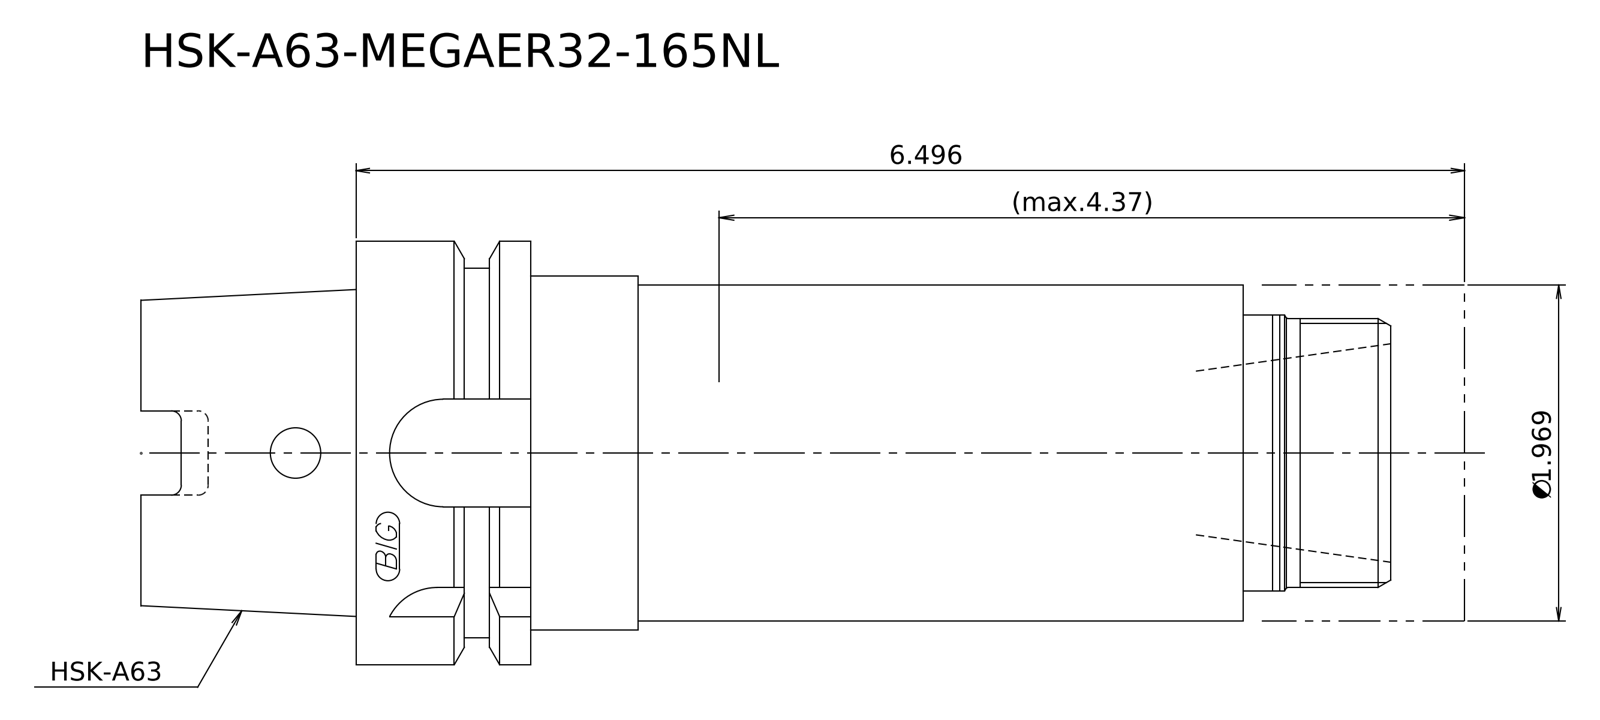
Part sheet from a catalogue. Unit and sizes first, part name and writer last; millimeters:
Units: millimetres
Overall size (bounding box): 197 × 63 × 63
Round bosses / shafts (diameter × count): ⌀63 ×1, ⌀55 ×1, ⌀52.6 ×1, ⌀50 ×1, ⌀41 ×1, ⌀40 ×1
Main face-to-face distances: 30.2, 197, 166.8, 165, 134.8, 32, 11, 19.2, 154, 186
Volume: 431 835 mm³ · Surface area: 44 918 mm²
Bodies: 2 solids, 23 faces (10 planar, 8 cylindrical, 5 other)
STEP written by: Kubotek KeyCreator 2011 V10.0.2 (22737) (automotive_design)
